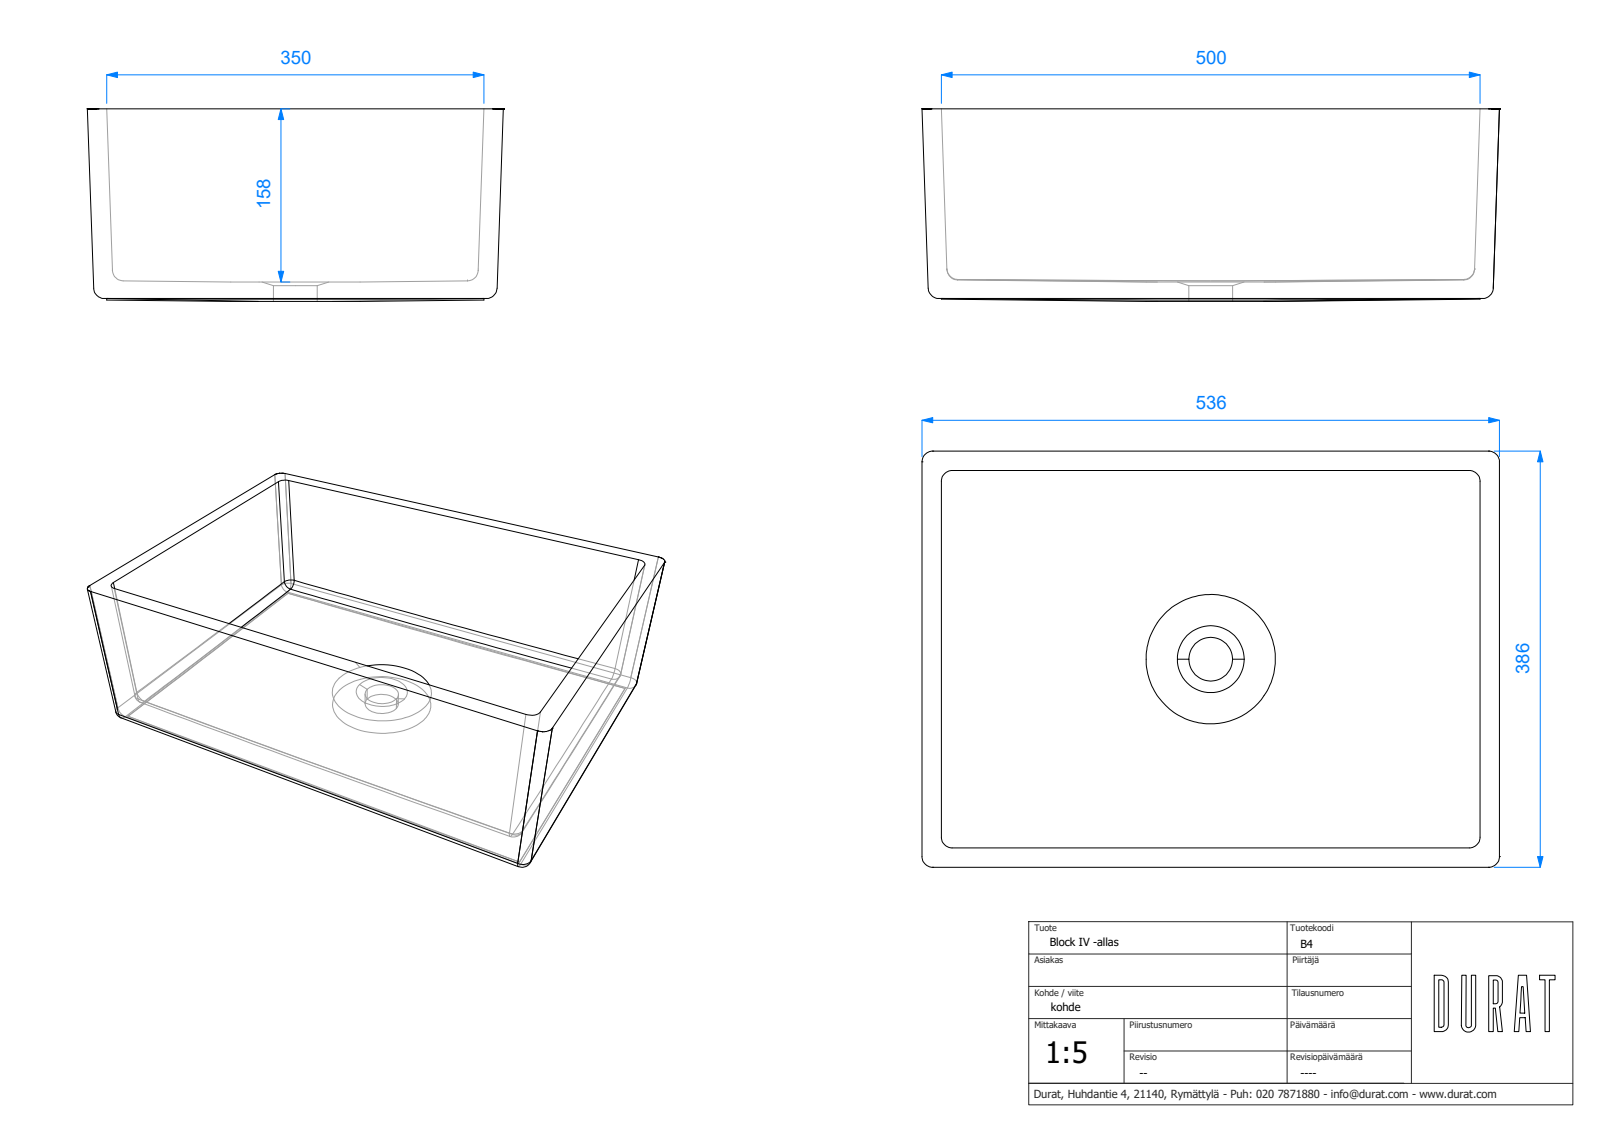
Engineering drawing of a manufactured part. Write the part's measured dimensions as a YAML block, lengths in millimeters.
step_written_by: "ST-DEVELOPER v15 (AUTOMOTIVE_DESIGN)"
units: millimeters
bodies: {solids: 0, faces: 48, planar: 16, cylindrical: 0, other: 32}
overall_size: [536.02, 386.02, 178.61]
face_to_face_distances: [17.97, 18.02, 18.01, 178.61, 18, 160.61, 2.61, 15.39, 176, 350]
